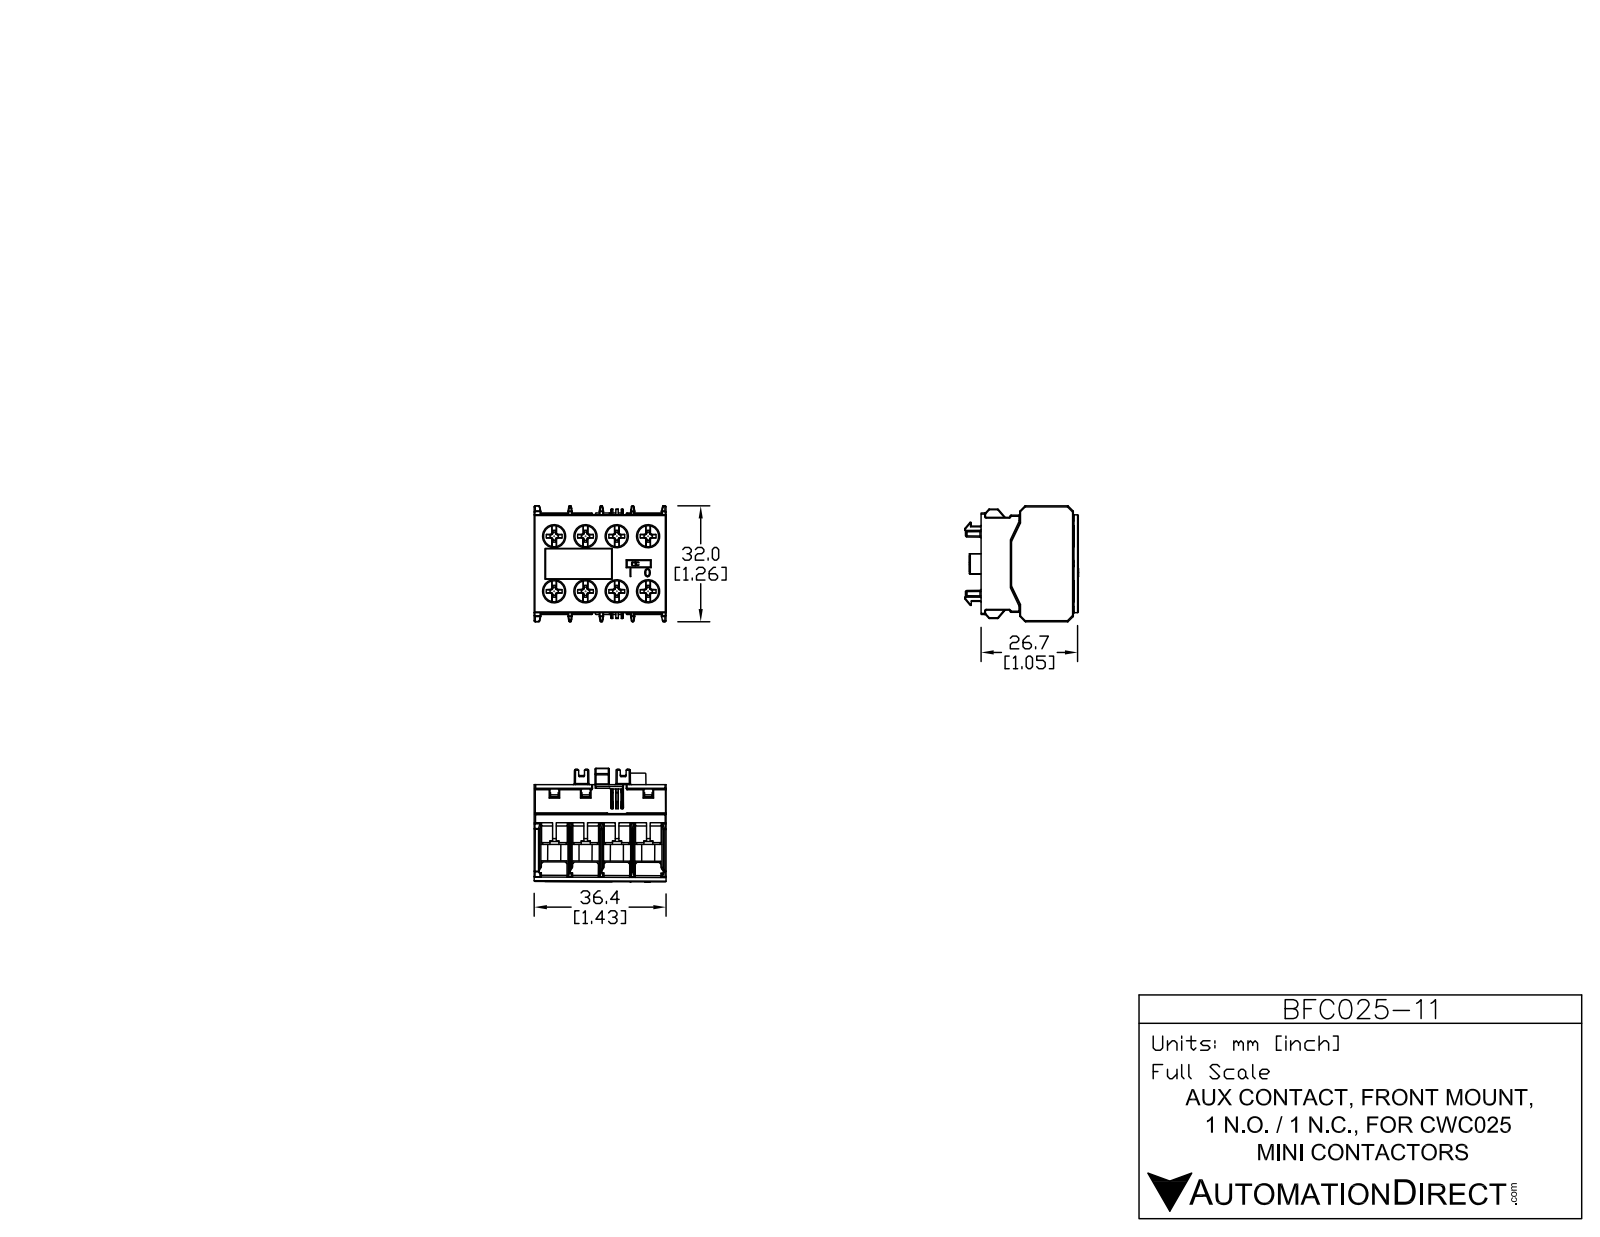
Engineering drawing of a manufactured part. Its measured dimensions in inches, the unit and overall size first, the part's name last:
Units: inches
Overall size (bounding box): 1.437 × 1.26 × 1.249
Round holes (diameter × count): ⌀0.236 ×8
Round bosses / shafts (diameter × count): ⌀0.197 ×8, ⌀0.118 ×8
Partial cylindrical surfaces — rounded edges, fillets, slot ends (radius × count): R0.008 ×58, R0.02 ×8, R0.178 ×8, R0.012 ×6, R0.01 ×4, R0.006 ×2, R0.007 ×2
Main face-to-face distances: 0.049, 0.34, 0.679, 0.339, 0.63, 0.389, 0.291, 0.314, 1.019, 1.437
Hole centre spacings: 0.34, 0.591, 0.679, 0.681, 0.9, 0.339, 0.681, 1.019
Volume: 1.6 in³ · Surface area: 37.1 in²
Bodies: 24 solids, 1105 faces (763 planar, 278 cylindrical, 64 other)
Part name (STEP PRODUCT): BFC025-11
STEP written by: SolidWorks 2013 (AUTOMOTIVE_DESIGN)
